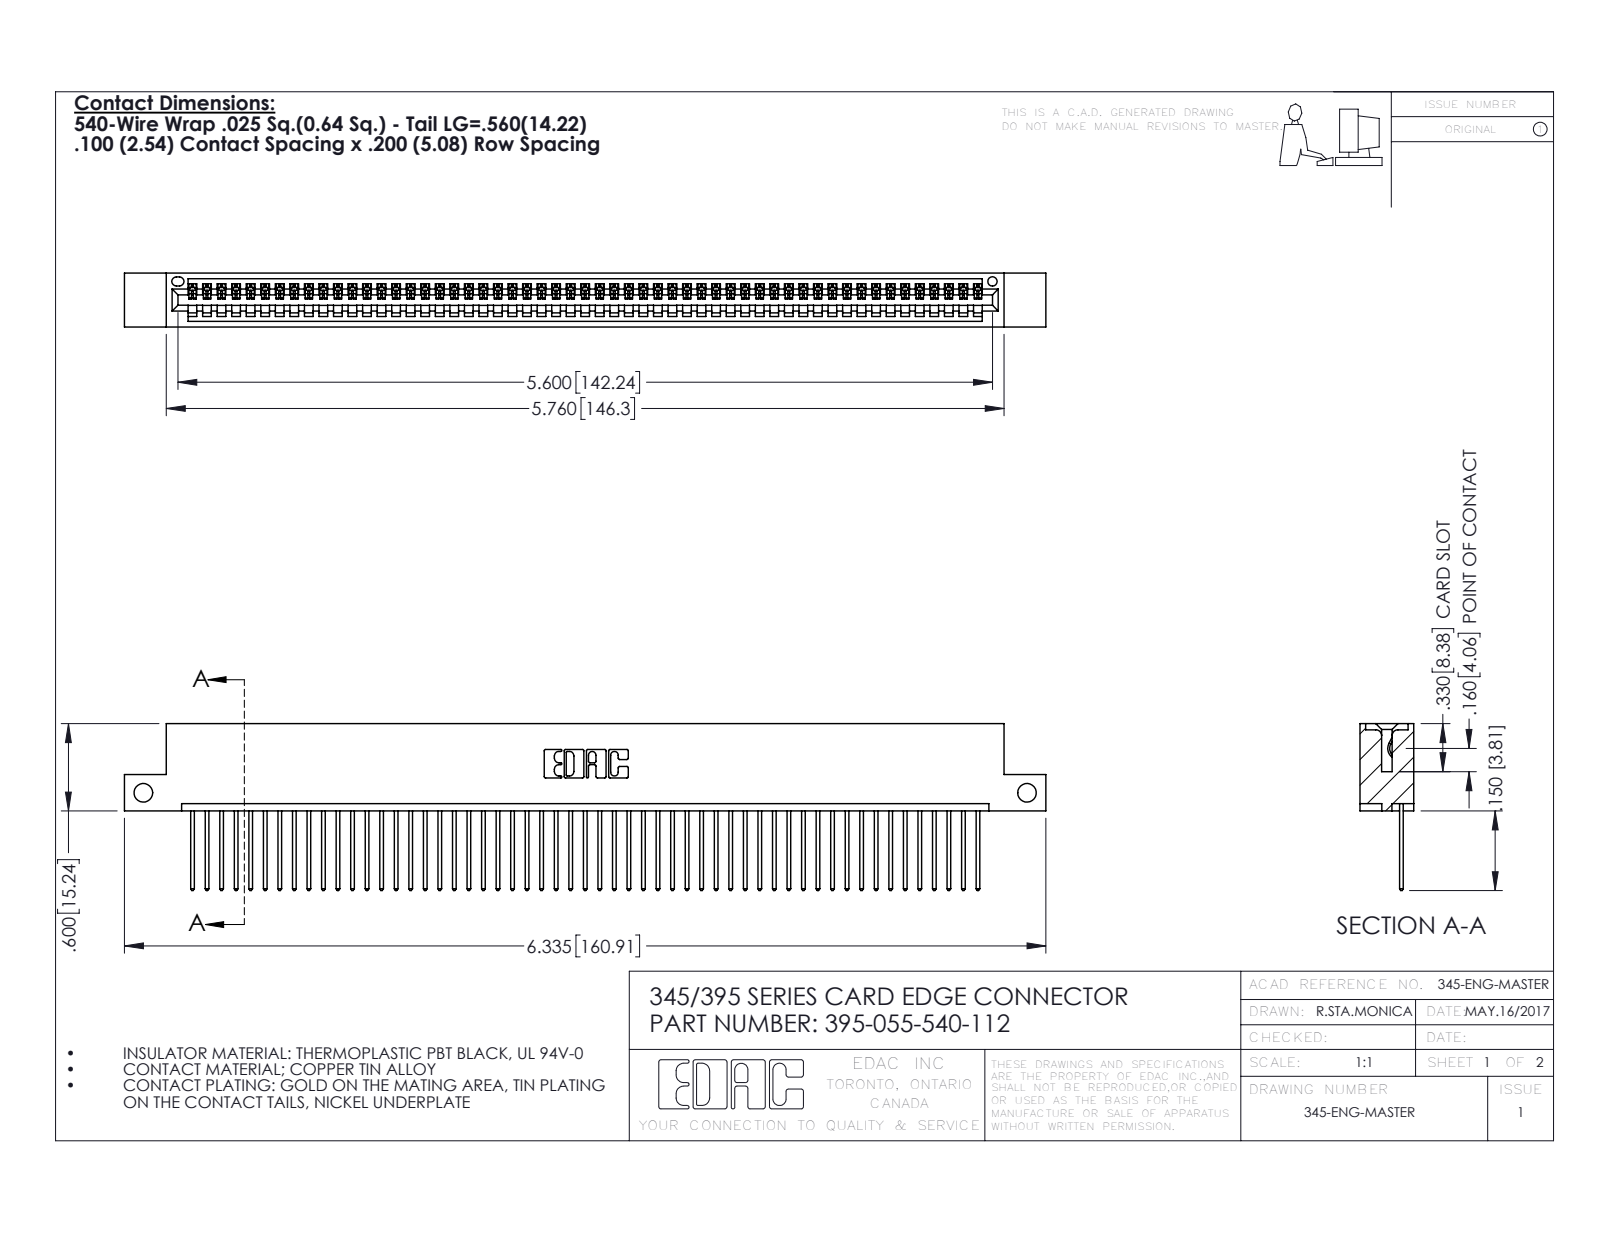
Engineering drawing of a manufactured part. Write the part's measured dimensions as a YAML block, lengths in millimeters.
part_name: "345 Part_Flush Mounting Lugs - Side Mount; 395-055-540-112; 345-292-001_345-293-140"
step_written_by: "SolidWorks 2016 (CONFIG_CONTROL_DESIGN)"
units: millimeters
bodies: {solids: 56, faces: 3316, planar: 2280, cylindrical: 1036, other: 0}
overall_size: [160.9, 29.1, 9.4]
volume: 15400
surface_area: 21010
round_holes:
  - {diameter: 3.3, count: 2}
  - {diameter: 1.6, count: 1}
partial_cylinders:
  - {radius: 0.2, count: 110}
  - {radius: 0.3, count: 110}
  - {radius: 0.3, count: 22}
  - {radius: 0.2, count: 6}
  - {radius: 0.8, count: 6}
  - {radius: 0.7, count: 3}
  - {radius: 0.8, count: 2}
  - {radius: 1, count: 2}
face_to_face_distances: [7.6, 1.8, 9.4, 2.5, 6.9, 0.6, 5.1, 5.7, 3.8, 1.8]
hole_center_spacings: [154.3]
